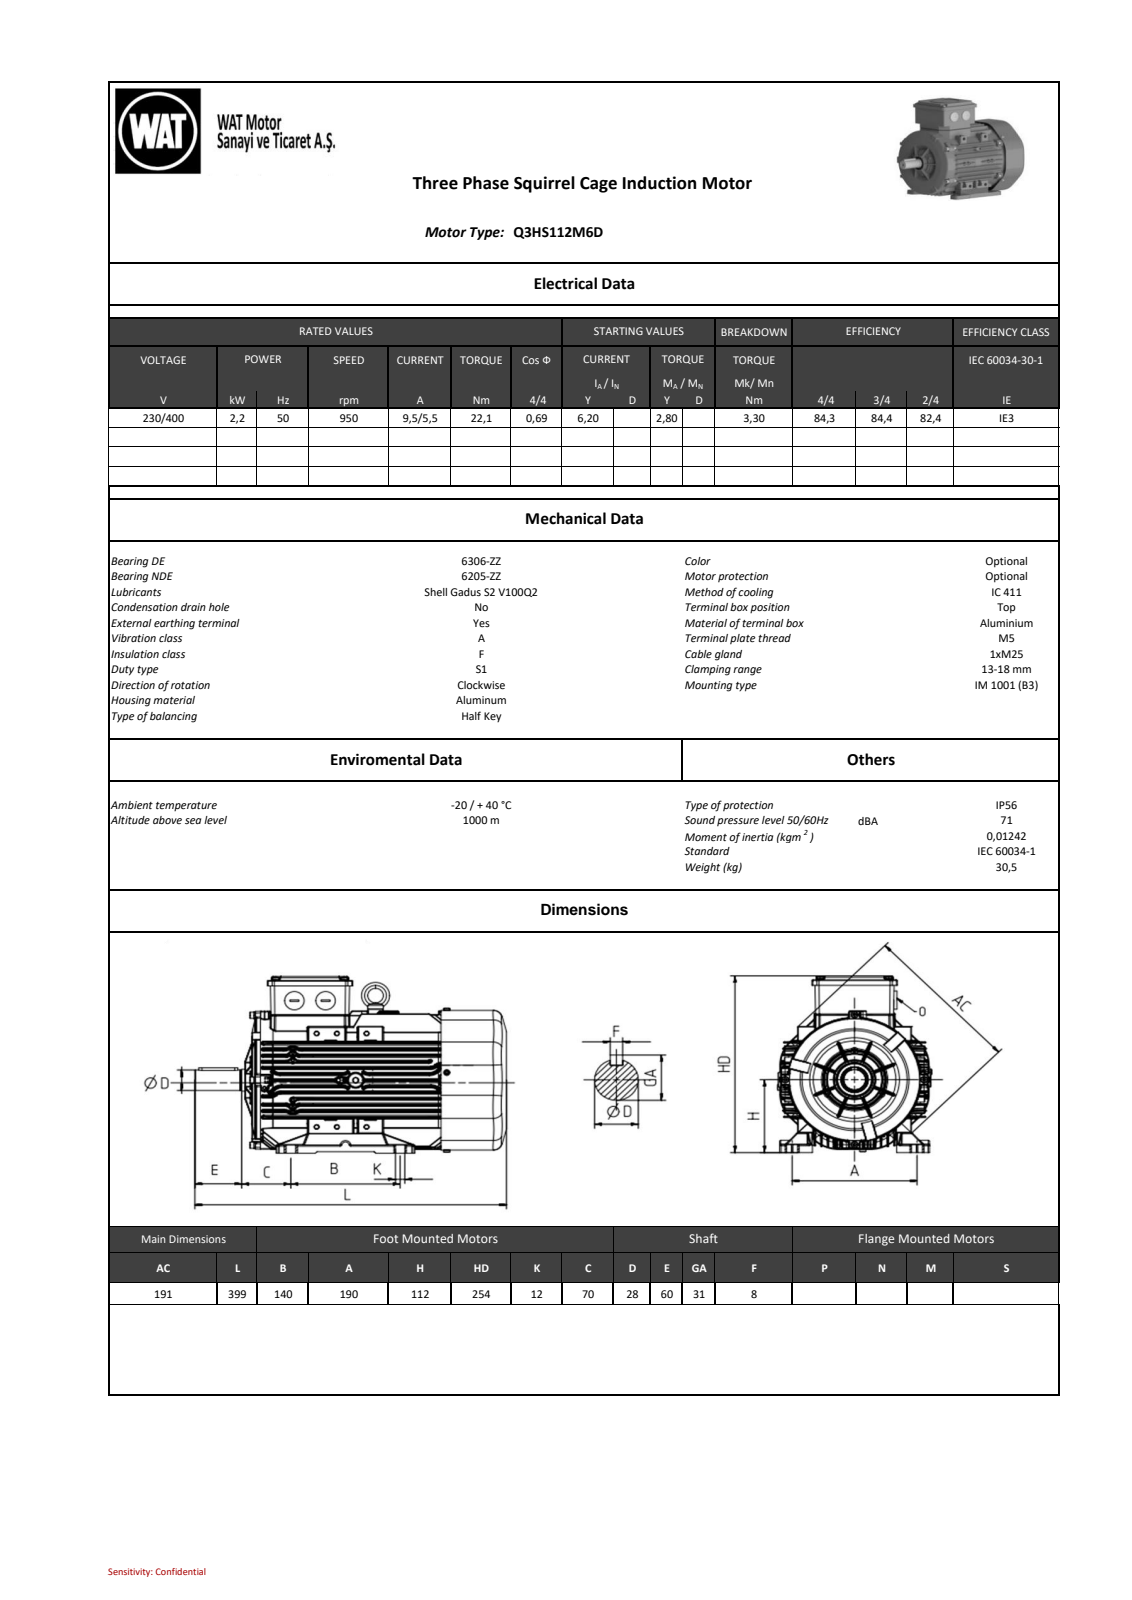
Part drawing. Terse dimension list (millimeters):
name: QHS Series_ 112_B3_stp_objects
written by: SIEMENS PLM Software NX2206.8101 (AUTOMOTIVE_DESIGN)
unit: mm
bodies: 0 solids, 6794 faces (1558 planar, 2782 cylindrical, 2454 other)
size: 399.31 × 255.22 × 221.93
holes: 1× ⌀10, 1× ⌀21.2, 1× ⌀44.42, 1× ⌀57.4, 1× ⌀89, 1× ⌀109, 1× ⌀129, 1× ⌀133
bosses: 8× ⌀8, 4× ⌀9.3, 4× ⌀8.5, 4× ⌀5, 3× ⌀25, 1× ⌀113.5, 1× ⌀93.5, 1× ⌀60.74
rounds: 721× R1, 662× R0.8, 115× R0.5, 108× R0.75, 98× R2, 49× R0.81, 44× R5, 26× R15
face distances: 8.53, 8.46, 8.45, 76.24, 16.91, 93.45, 76.68, 17.05, 25.58, 59.63
